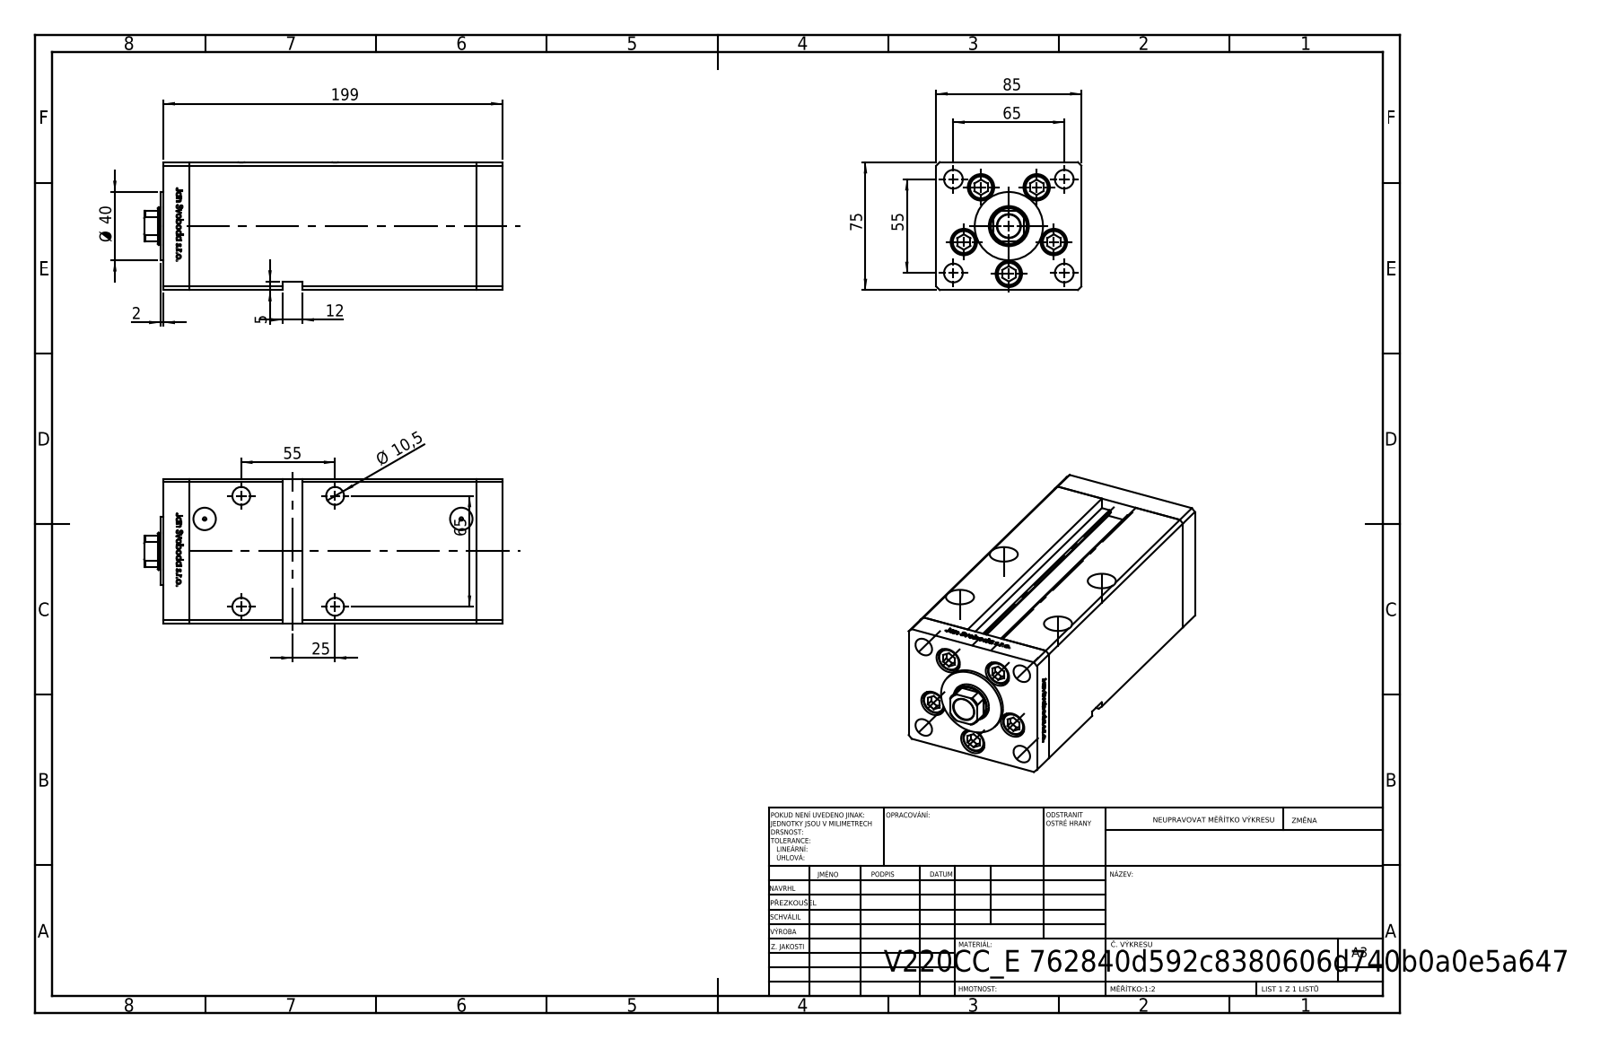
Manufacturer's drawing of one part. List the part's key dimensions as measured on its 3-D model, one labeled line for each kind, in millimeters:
Part name (STEP PRODUCT): V220C_FRONT_E; V220C BACK_E; V220C_VC_E; V220C_E MIDDLE (+1 more)
STEP written by: SolidWorks 2019 (CONFIG_CONTROL_DESIGN)
Units: millimetres
Bodies: 14 solids, 1214 faces (475 planar, 165 cylindrical, 574 other)
Overall size (bounding box): 210 × 85 × 75
Volume: 1 076 000 mm³ · Surface area: 182 851 mm²
Round holes (diameter × count): ⌀11 ×9, ⌀15.5 ×5, ⌀10.5 ×4, ⌀16.5 ×4, ⌀2 ×2, ⌀13.16 ×2, ⌀13.5 ×1, ⌀22 ×1, ⌀23.5 ×1
Round bosses / shafts (diameter × count): ⌀14.5 ×5, ⌀8 ×5, ⌀40 ×1
Partial cylindrical surfaces — rounded edges, fillets, slot ends (radius × count): R0.93 ×2, R10.5 ×1
Main face-to-face distances: 85, 75, 15, 168.5, 183.5, 198.5, 34.25, 68.5, 10.5, 19.25
Hole centre spacings: 28, 42.57, 55, 65, 85.15, 16.86, 19.17, 32.33
